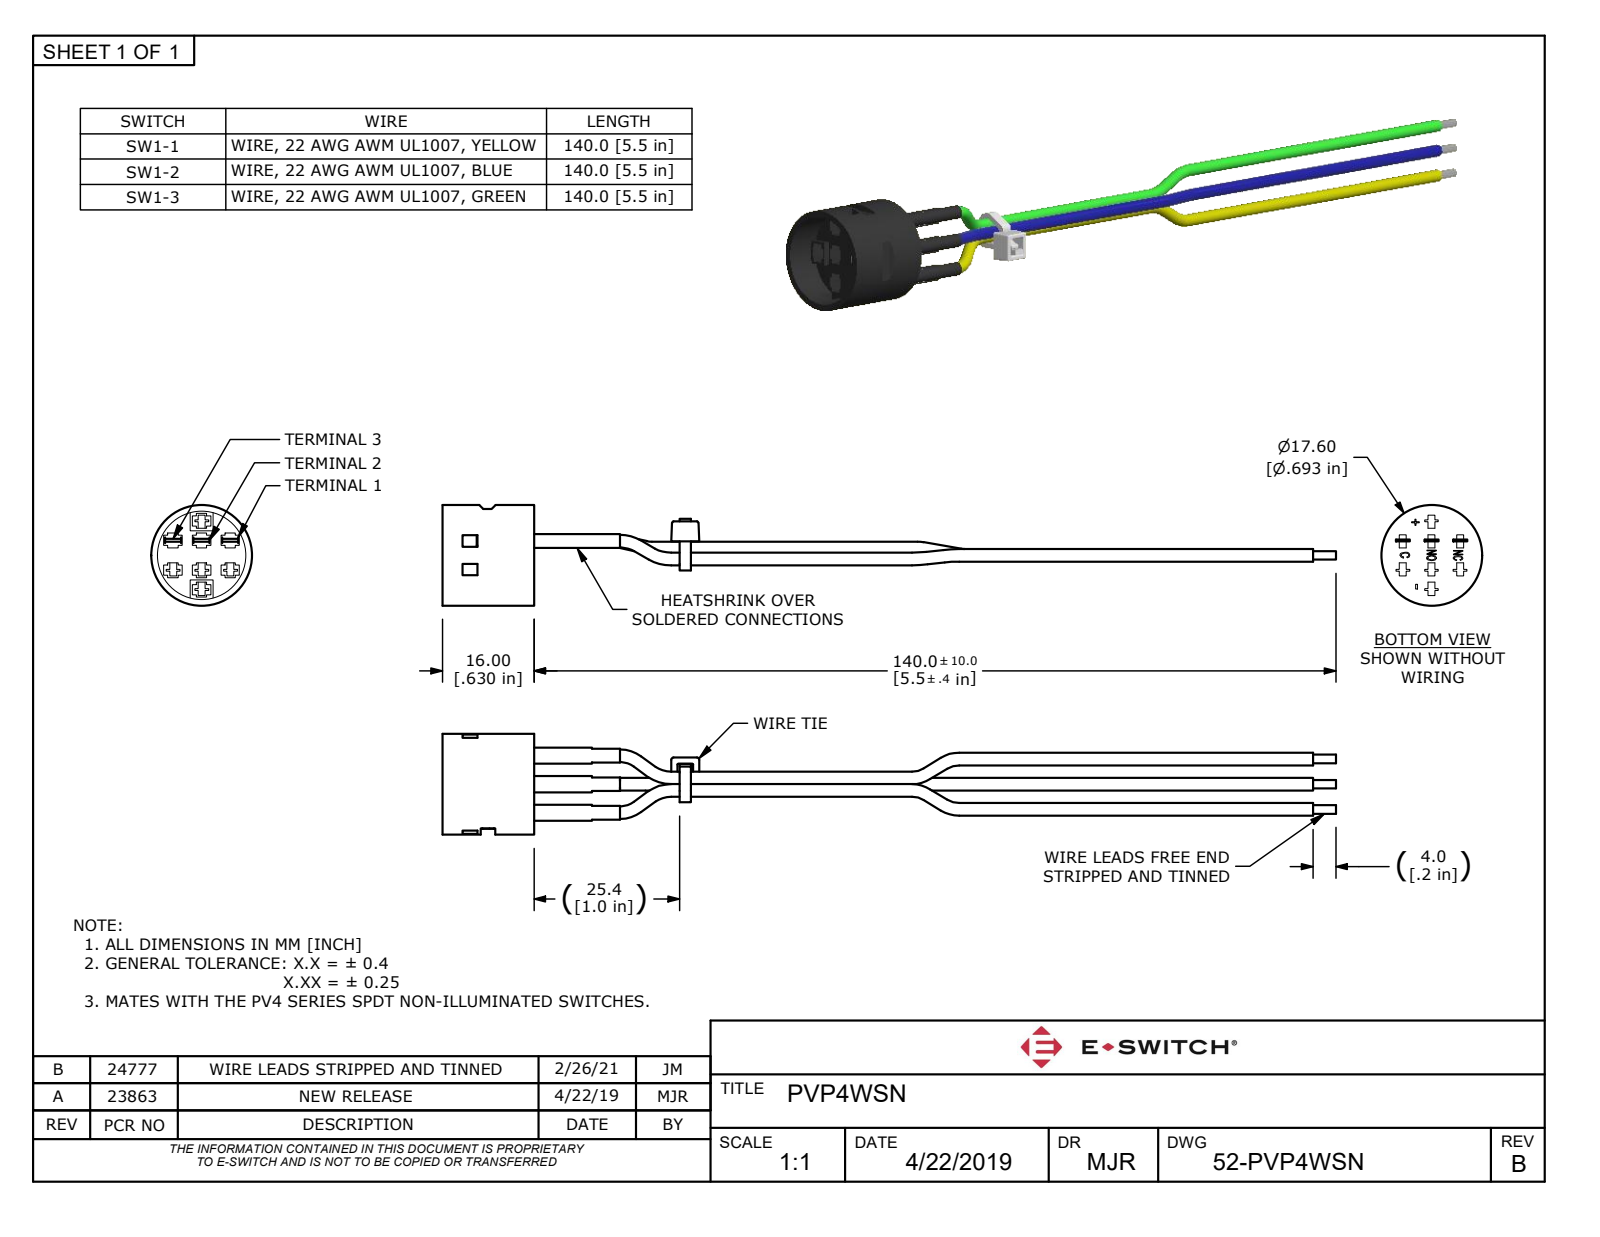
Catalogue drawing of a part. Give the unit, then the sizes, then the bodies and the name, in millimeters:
Units: millimetres
Overall size (bounding box): 156 × 17.6 × 17.6
Round holes (diameter × count): ⌀2.2 ×3, ⌀15.4 ×1
Round bosses / shafts (diameter × count): ⌀2.2 ×12, ⌀2.4 ×3, ⌀1.5 ×3, ⌀17.6 ×1
Partial cylindrical surfaces — rounded edges, fillets, slot ends (radius × count): R0.2 ×14, R0.25 ×10, R1.1 ×5, R0.75 ×3, R2 ×1
Main face-to-face distances: 2.2, 0.5, 0.4, 1.8, 2.5, 5, 9.9, 3.2, 8.6, 3
Hole centre spacings: 5, 5.59, 2.5, 10
Volume: 3 979 mm³ · Surface area: 6 047 mm²
Bodies: 1 solid, 621 faces (463 planar, 71 cylindrical, 87 other)
Part name (STEP PRODUCT): PVP4WSN
STEP written by: Autodesk Inventor 2018 (AP242_MANAGED_MODEL_BASED_3D_ENGINEERING_MIM_LF)
